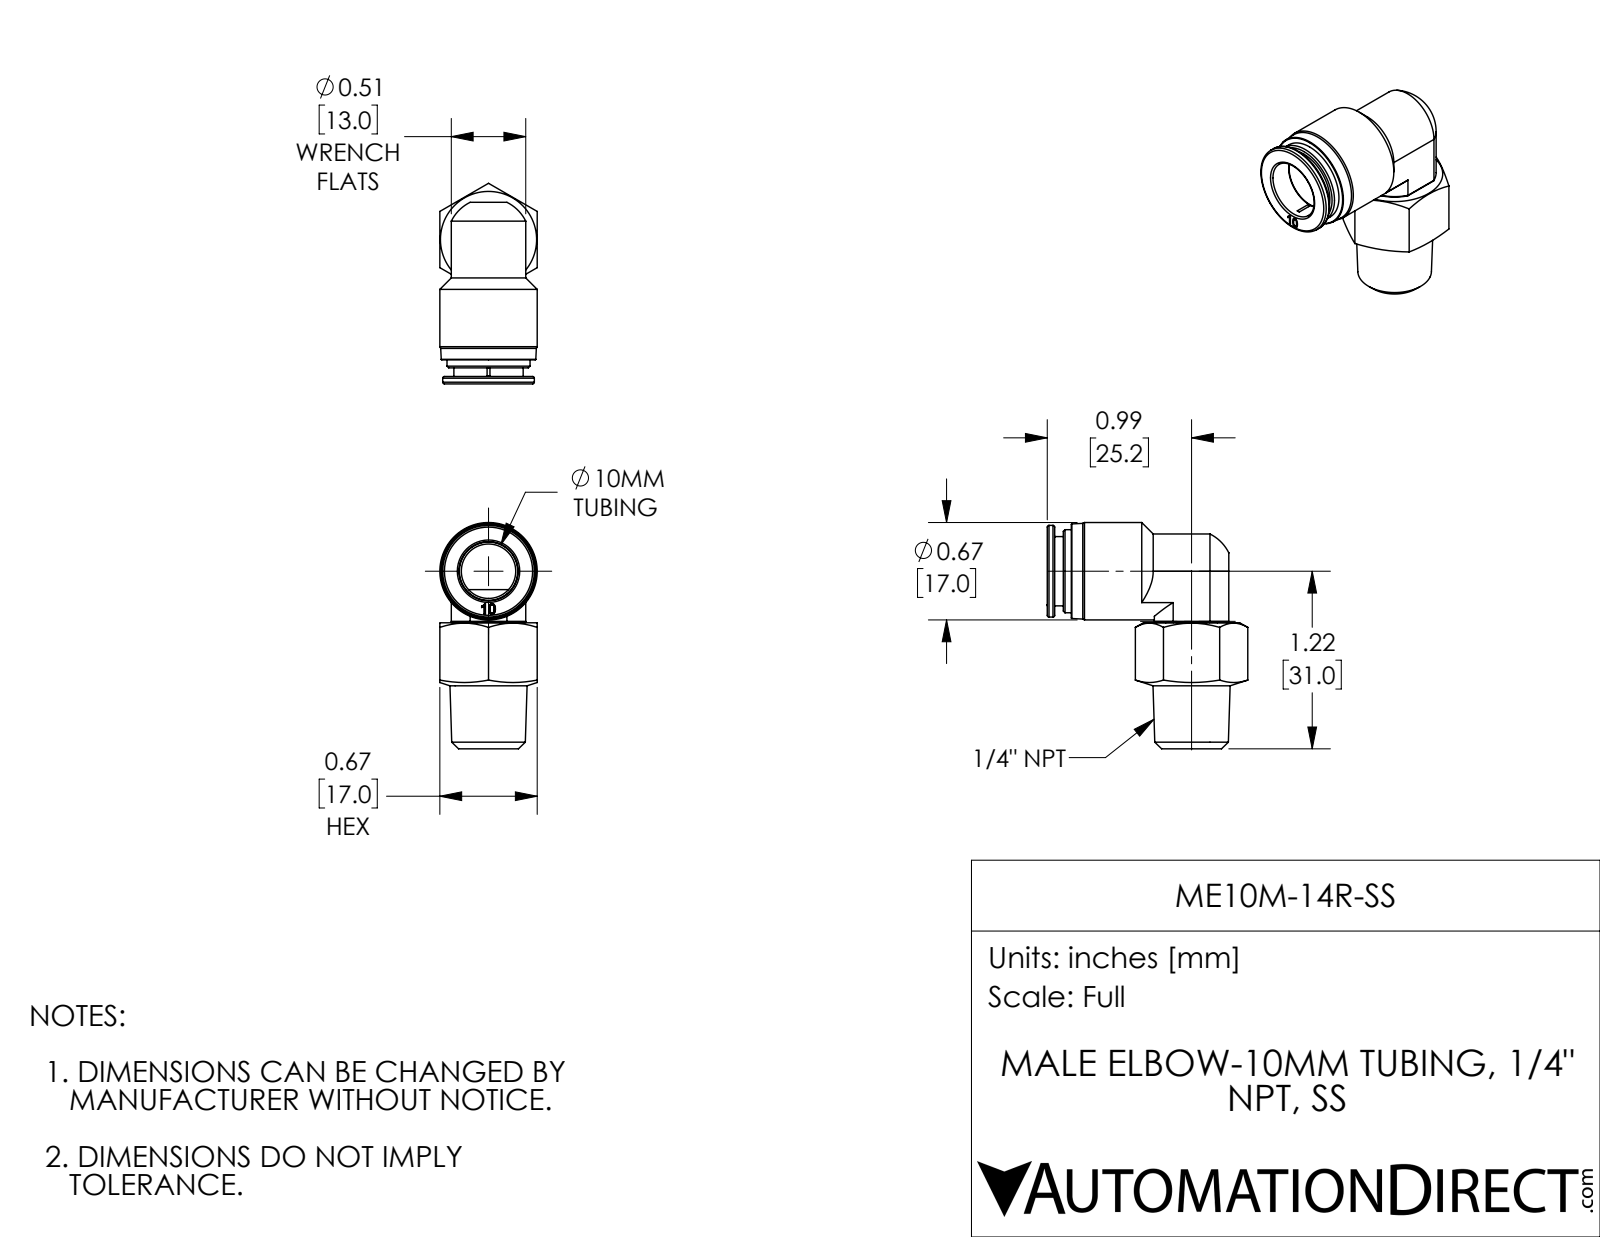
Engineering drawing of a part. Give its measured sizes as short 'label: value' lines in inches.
name: ME10M-14R-SS
written by: SolidWorks 2017 (AUTOMOTIVE_DESIGN)
unit: in
bodies: 2 solids, 112 faces (35 planar, 31 cylindrical, 46 other)
size: 1.555 × 1.379 × 0.669
volume: 0.422 in³; area: 8.571 in²
holes: 1× ⌀0.276, 1× ⌀0.356, 1× ⌀0.374, 1× ⌀0.402, 1× ⌀0.406
bosses: 1× ⌀0.669, 1× ⌀0.63, 1× ⌀0.571, 1× ⌀0.476, 1× ⌀0.354
rounds: 4× R0.008, 1× R0.256, 1× R0.285
face distances: 0.669, 0.079, 0.591, 0.512, 1.248, 0.051, 1.197, 0.165, 0.114, 1.083
